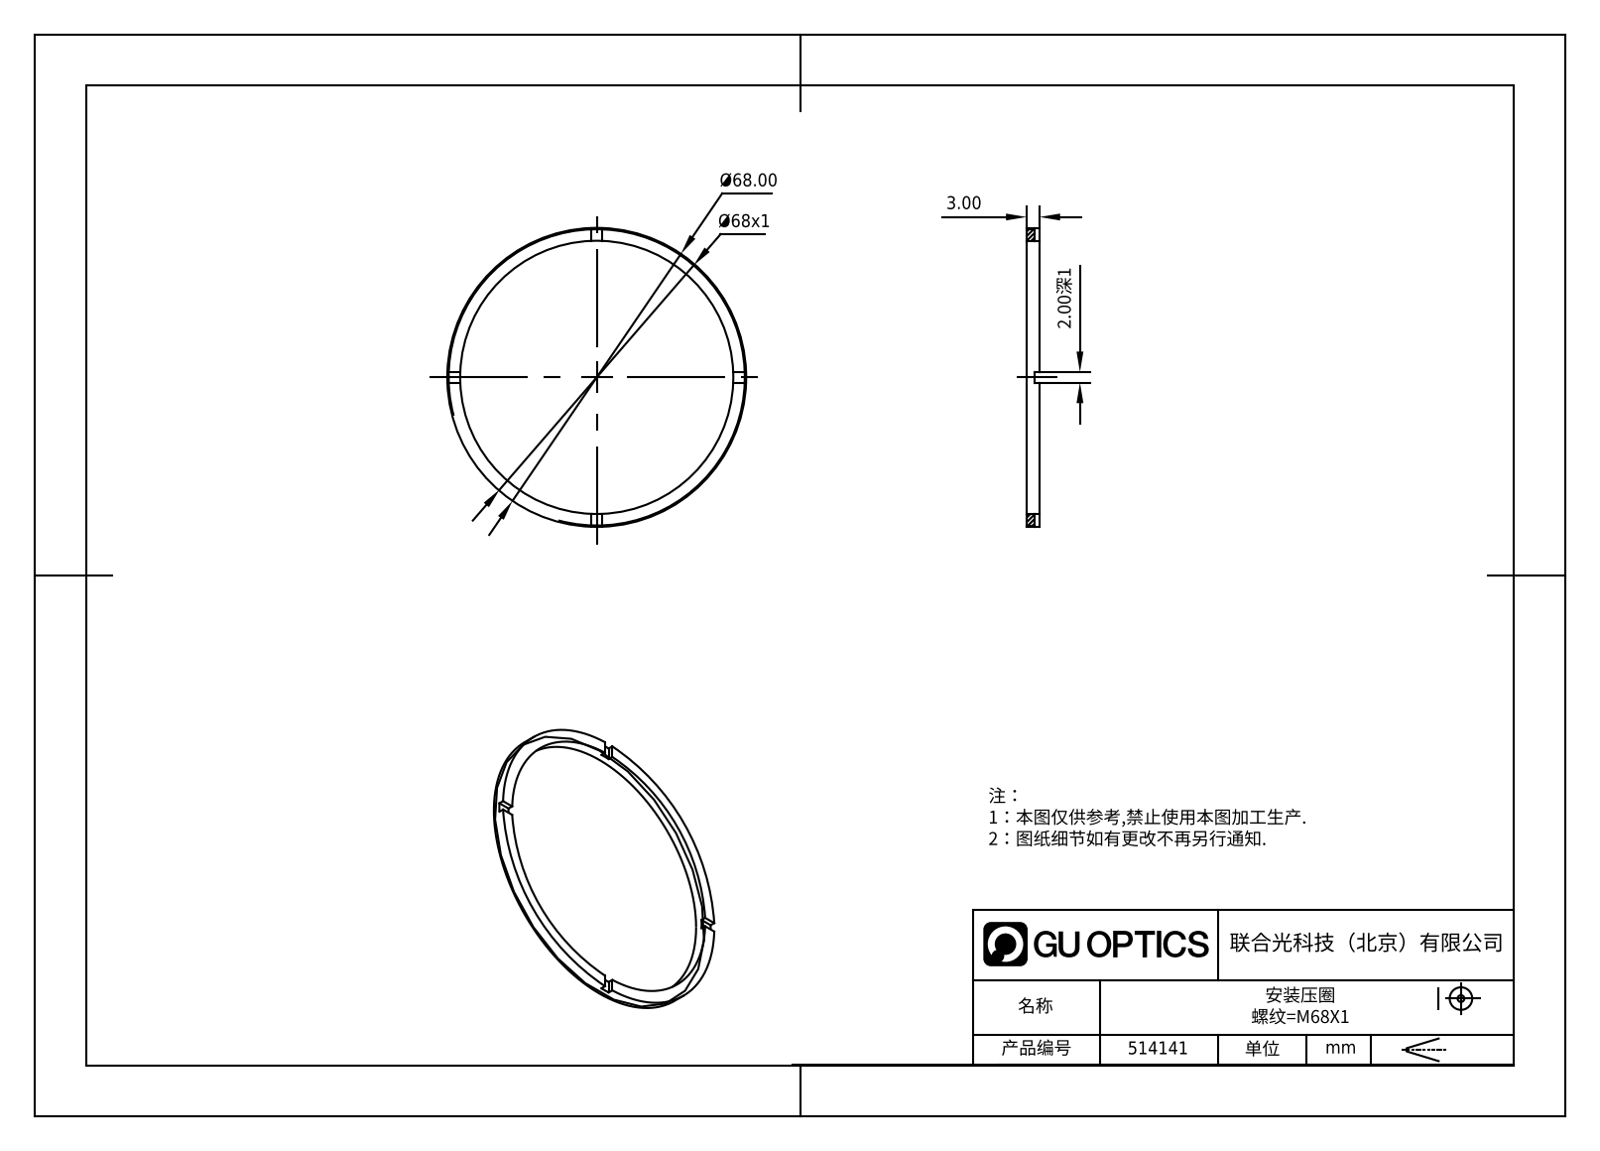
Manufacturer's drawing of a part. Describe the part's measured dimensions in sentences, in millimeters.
The part is named "514141". Its 3-D file was written by "SolidWorks 2020 (CONFIG_CONTROL_DESIGN)". It is 1 solid with 21 faces: 17 planar, 4 cylindrical and 0 other. Overall it measures 68 by 68 by 3 millimeters. Its volume is 1 523 cubic millimeters and its surface area 2 268 square millimeters. Round holes: 1 of diameter 63. Round bosses or shafts: 1 of diameter 68. The main face-to-face distances are 3, 2, 1.
